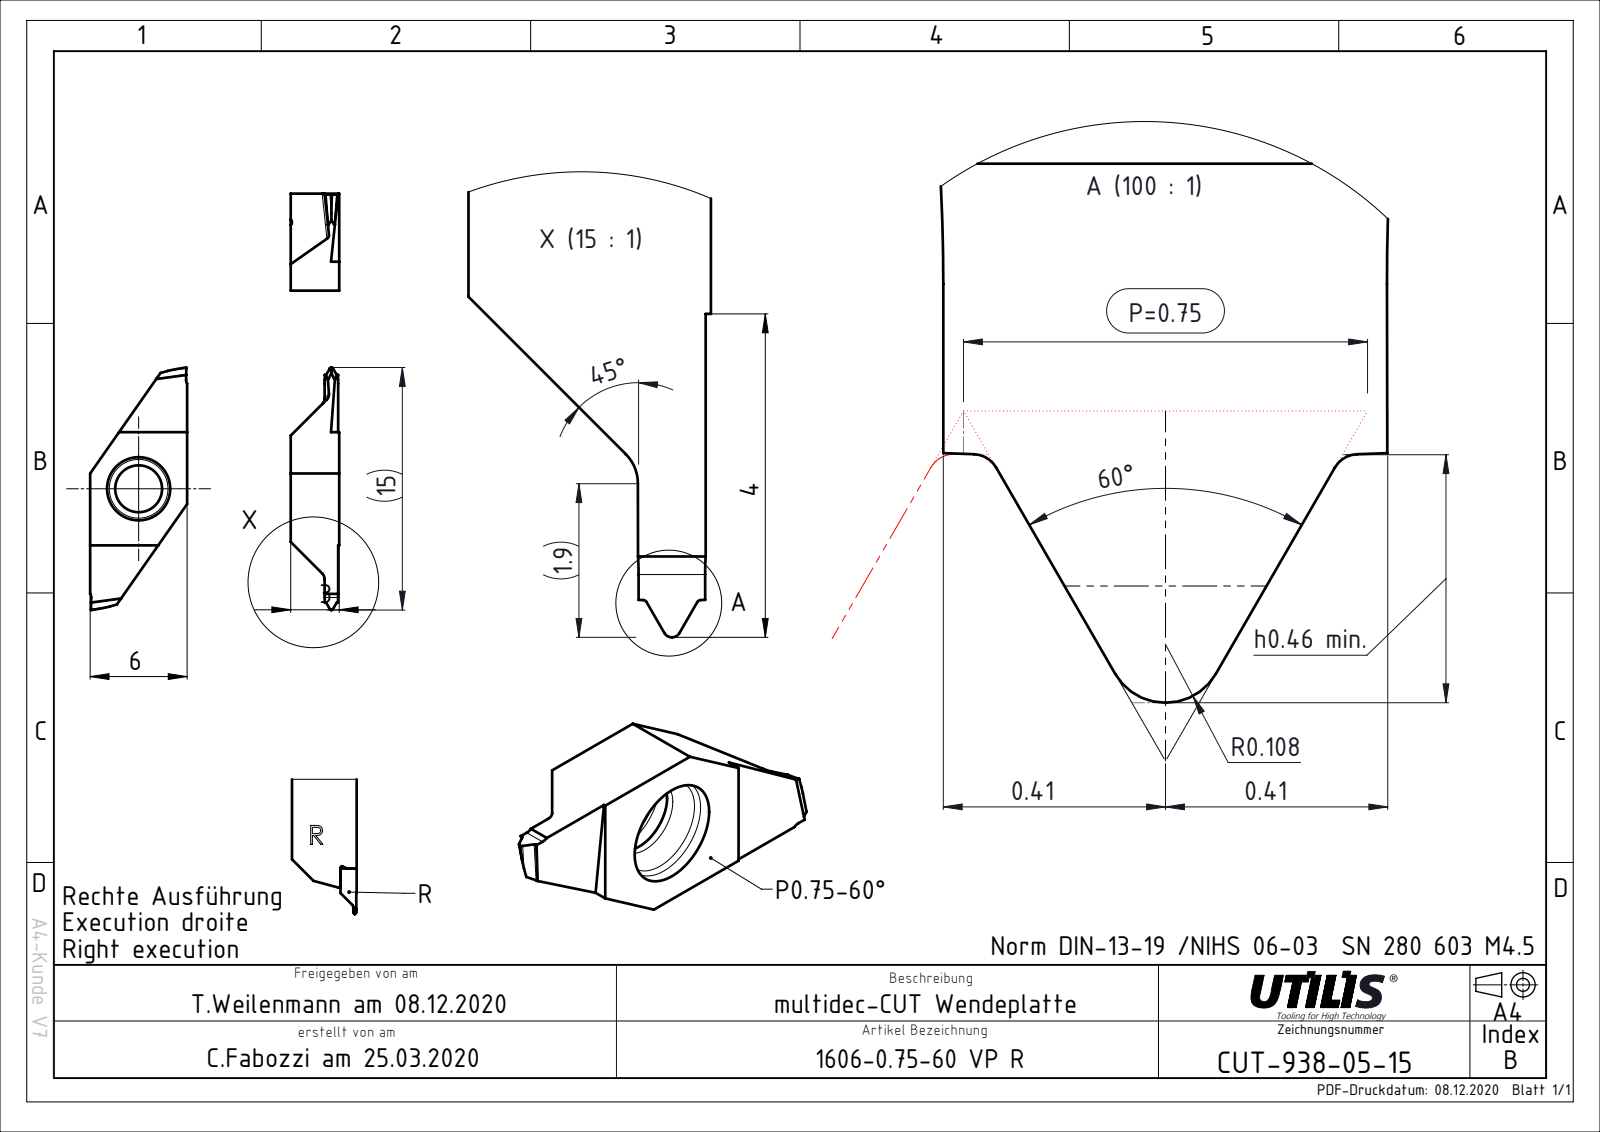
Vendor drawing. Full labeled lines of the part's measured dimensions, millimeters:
Part name (STEP PRODUCT): CUT-938-05; ASME Y14.5
STEP written by: FormatWorks Professional (AP242_MANAGED_MODEL_BASED_3D_ENGINEERING_MIM_LF)
Units: millimetres
Bodies: 1 solid, 43 faces (24 planar, 14 cylindrical, 5 other)
Overall size (bounding box): 15 × 6 × 3
Volume: 123 mm³ · Surface area: 209 mm²
Round holes (diameter × count): ⌀2.9 ×1
Partial cylindrical surfaces — rounded edges, fillets, slot ends (radius × count): R0.11 ×4, R0.5 ×2
Main face-to-face distances: 6, 3, 0.67, 11.22, 9, 12, 7, 12.61, 12.62
